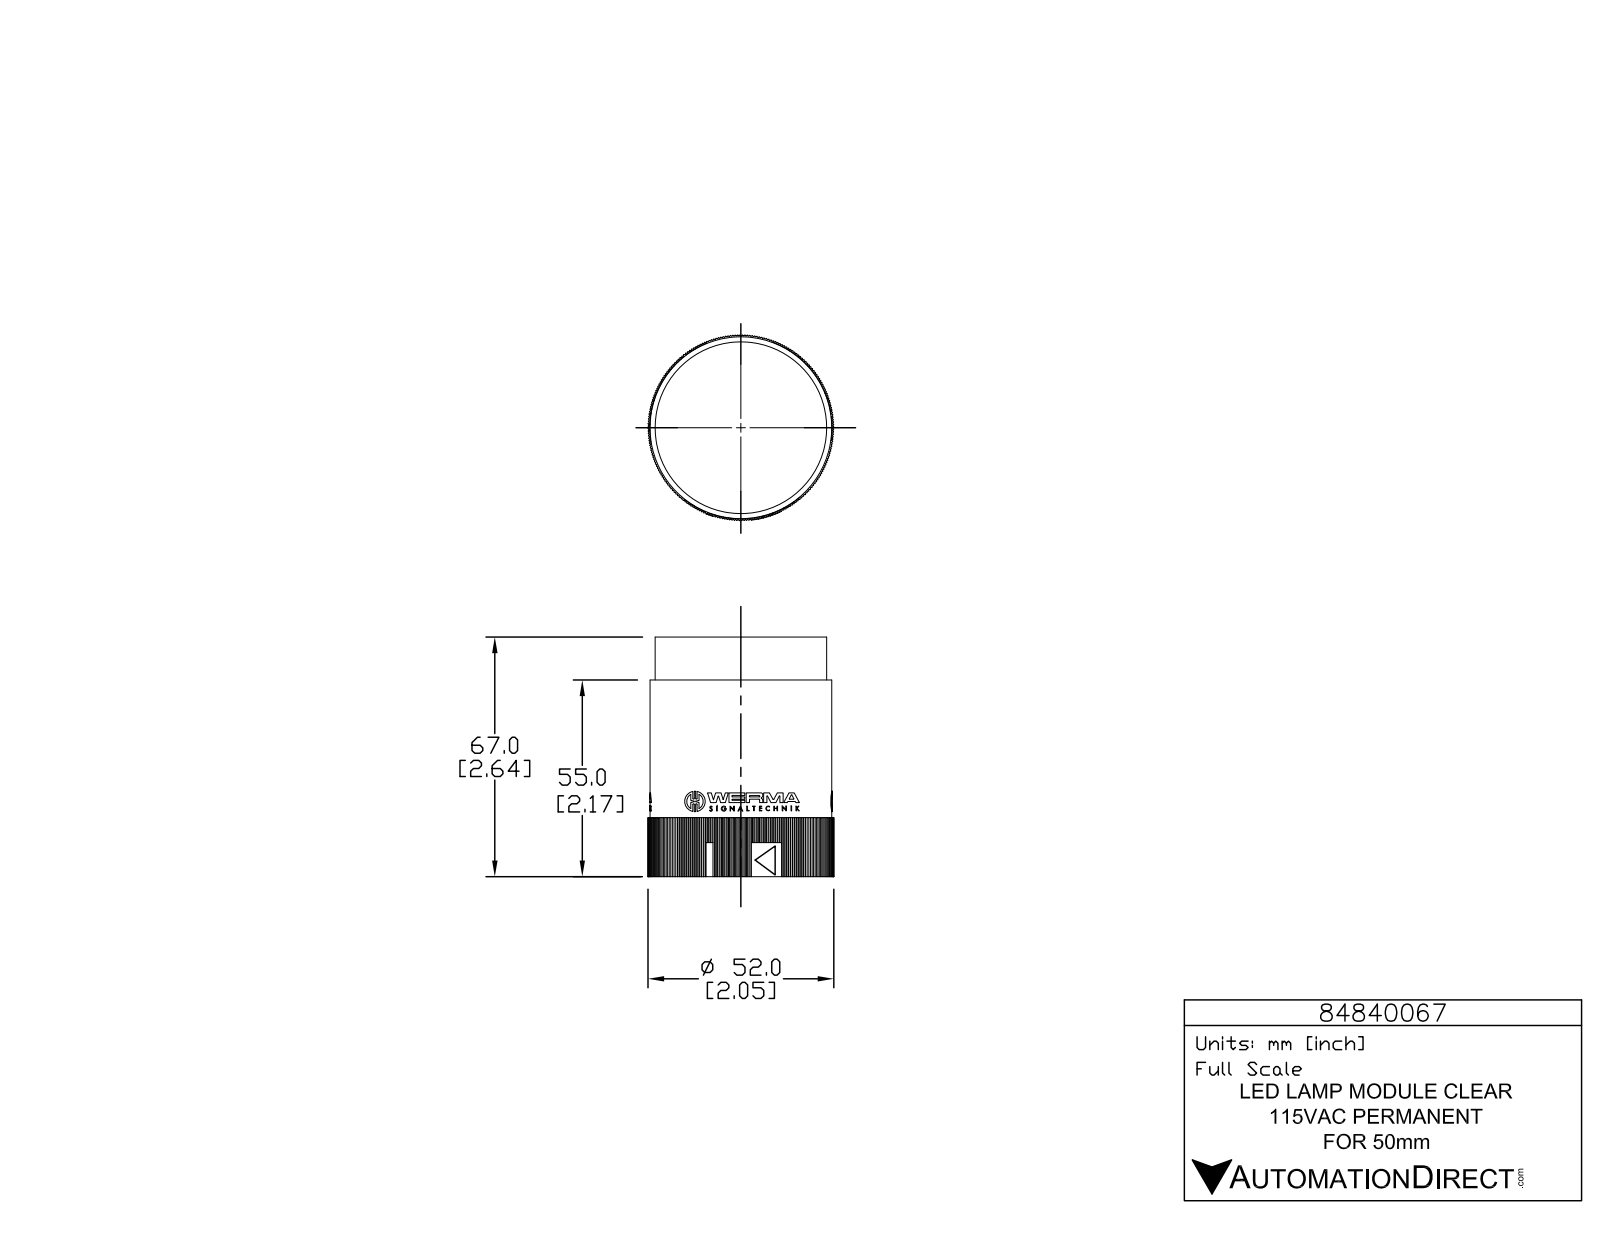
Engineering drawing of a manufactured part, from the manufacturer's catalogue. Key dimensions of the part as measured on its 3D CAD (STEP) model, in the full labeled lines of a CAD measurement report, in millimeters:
Part name (STEP PRODUCT): 84840067
STEP written by: SolidWorks 2015 (AUTOMOTIVE_DESIGN)
Units: millimetres
Bodies: 1 solid, 1265 faces (1020 planar, 245 cylindrical, 0 other)
Overall size (bounding box): 67 × 52 × 52
Volume: 112 600 mm³ · Surface area: 17 820 mm²
Round holes (diameter × count): ⌀1 ×3, ⌀48.2 ×1
Round bosses / shafts (diameter × count): ⌀5.7 ×3, ⌀1.4 ×3, ⌀50.9 ×1, ⌀48 ×1
Partial cylindrical surfaces — rounded edges, fillets, slot ends (radius × count): R0.2 ×6, R0.2 ×6, R0.2 ×6, R3.3 ×6, R0.1 ×3, R0.1 ×3, R0.2 ×3, R0.2 ×3
Main face-to-face distances: 55, 36.3, 36.3, 36.3, 12, 67, 36.3, 36.3, 43, 50.5
